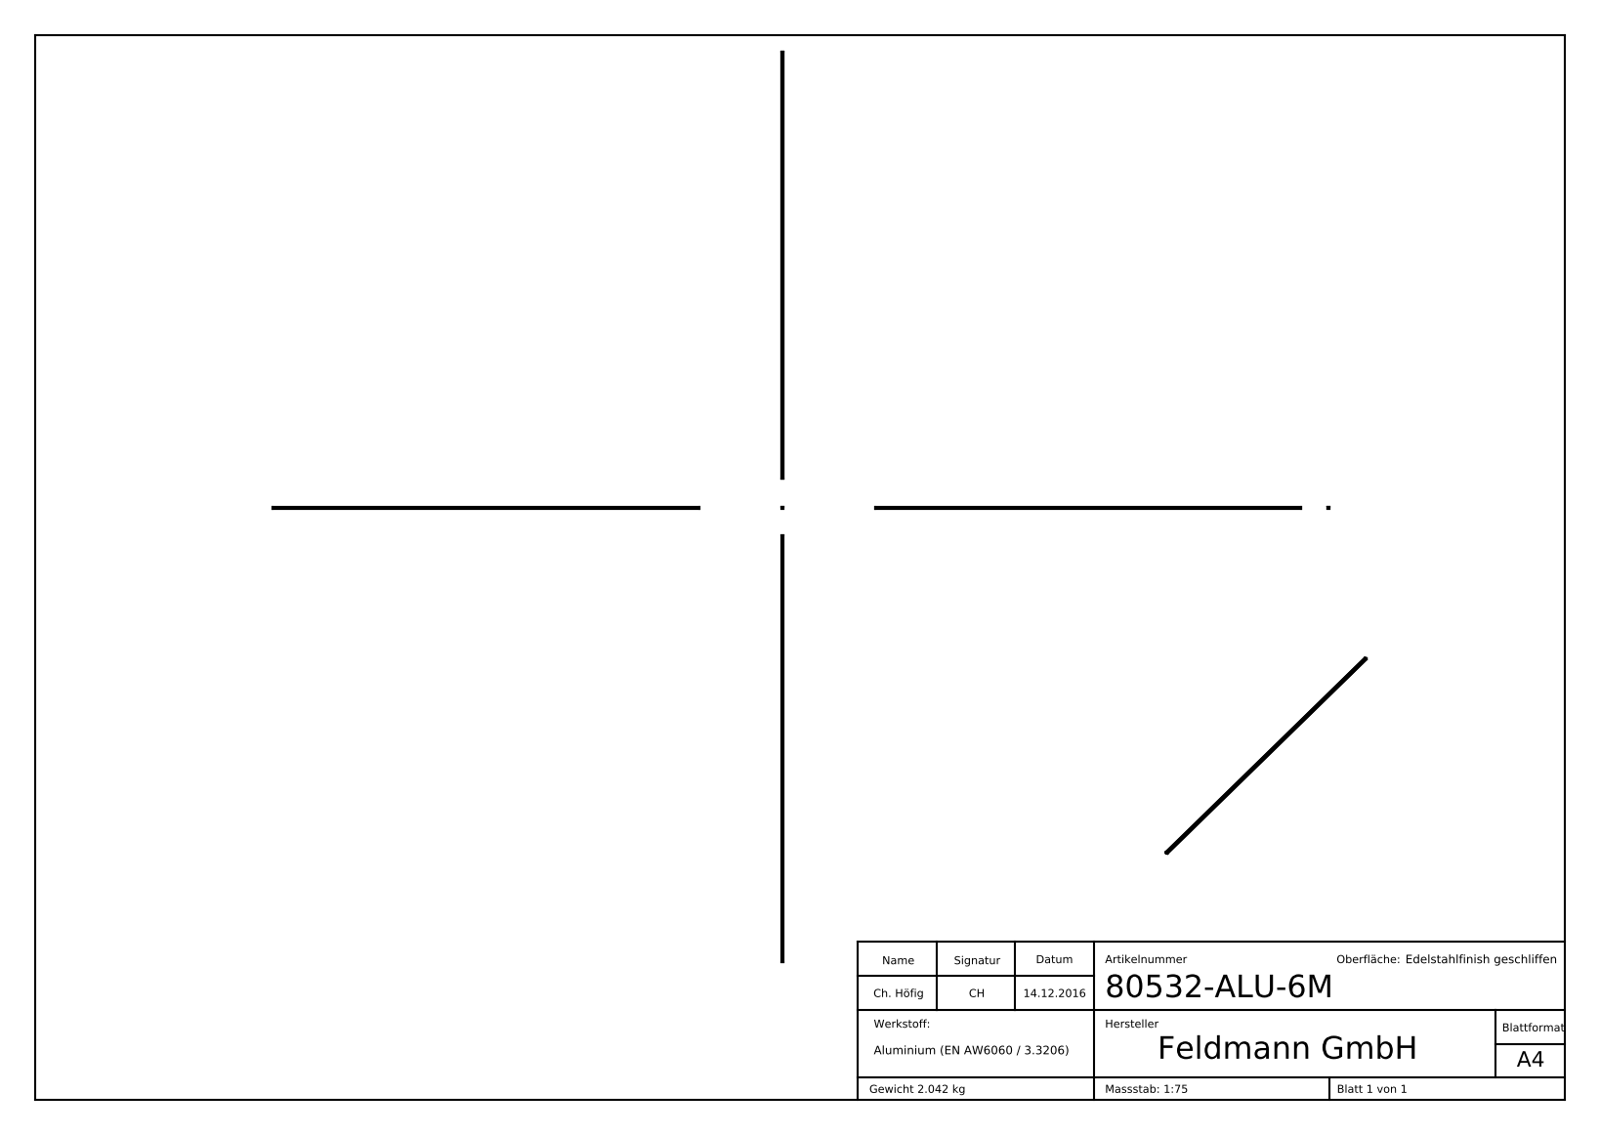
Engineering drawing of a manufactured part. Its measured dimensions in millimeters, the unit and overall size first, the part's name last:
Units: millimetres
Overall size (bounding box): 6000 × 28 × 20
Partial cylindrical surfaces — rounded edges, fillets, slot ends (radius × count): R0.5 ×4, R2 ×2
Main face-to-face distances: 2, 26, 28, 24, 18, 20, 6000, 1.9, 24.1, 26.1
Volume: 756 411 mm³ · Surface area: 776 812 mm²
Bodies: 1 solid, 283 faces (151 planar, 6 cylindrical, 126 other)
Part name (STEP PRODUCT): 80532-ALU-6M
STEP written by: SolidWorks 2015 (CONFIG_CONTROL_DESIGN)
